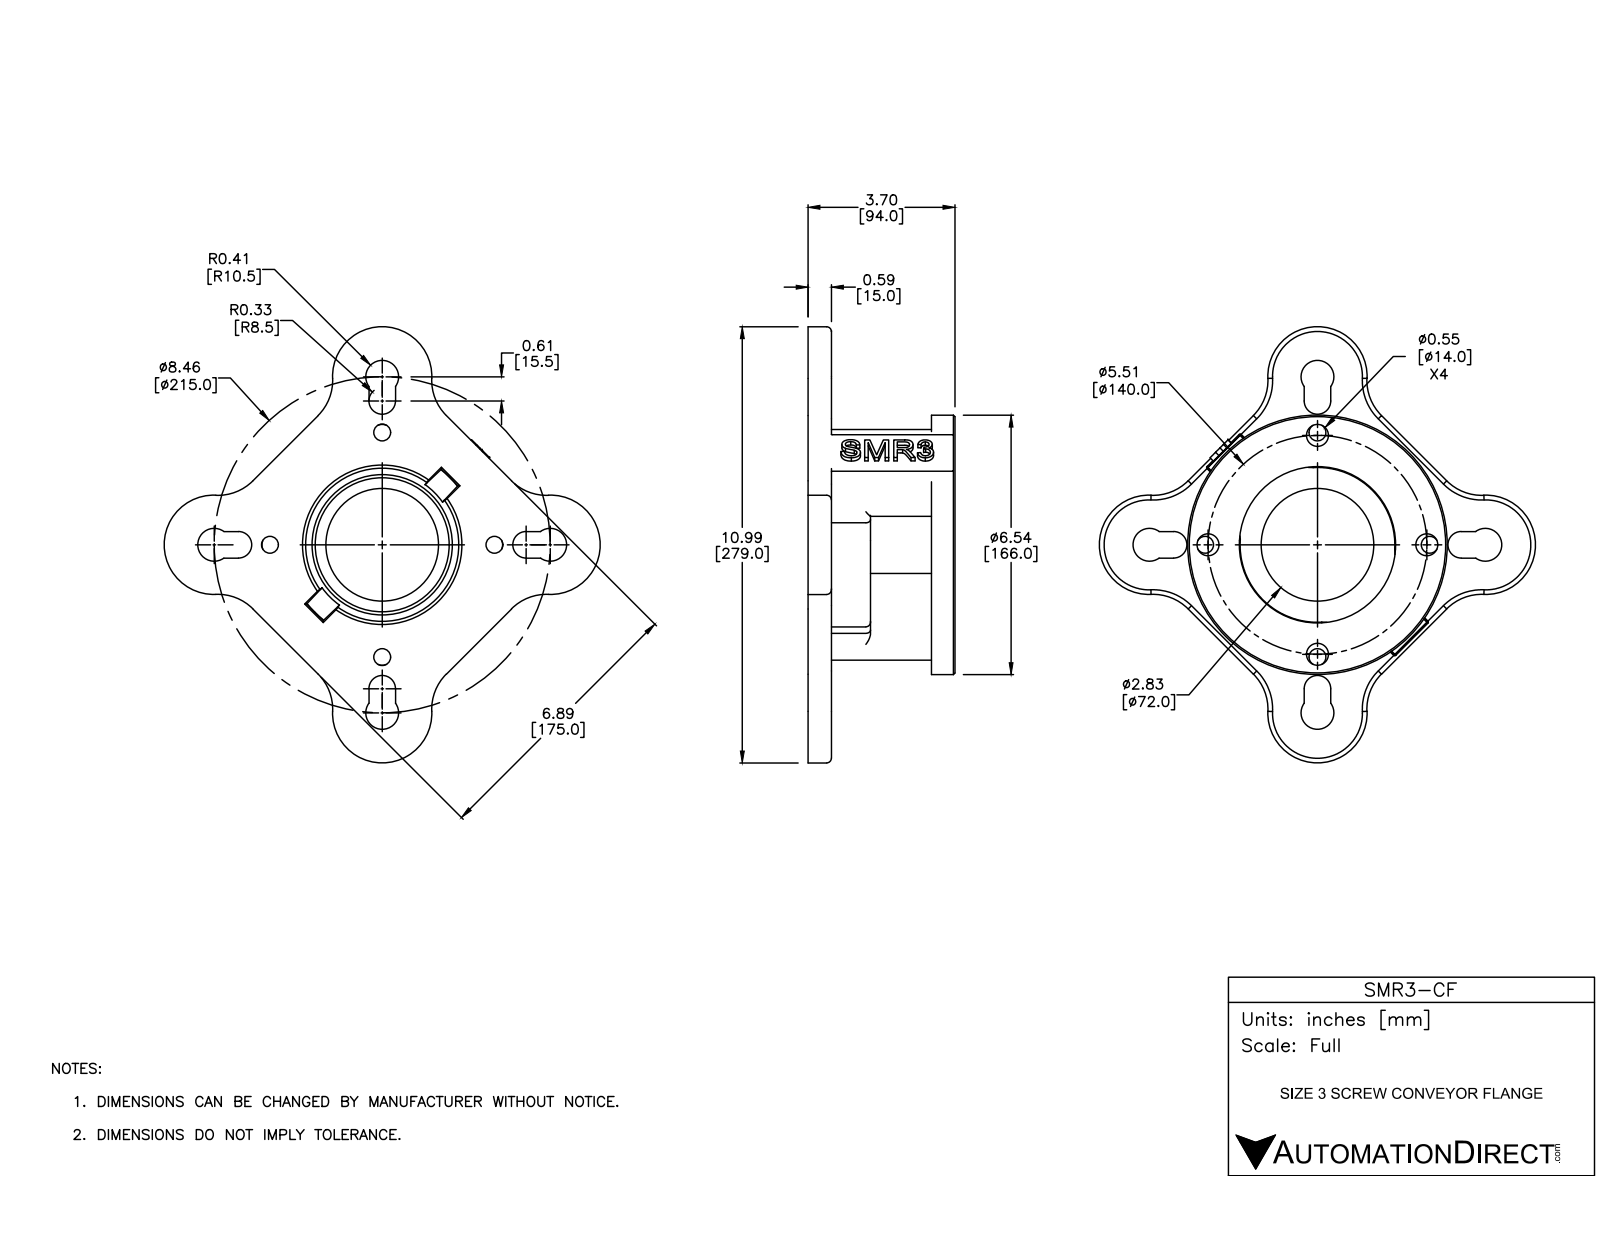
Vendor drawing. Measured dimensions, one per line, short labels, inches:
name: SMR3-CF
written by: SolidWorks 2016 (AUTOMOTIVE_DESIGN)
unit: in
bodies: 1 solid, 267 faces (79 planar, 104 cylindrical, 84 other)
size: 10.985 × 10.985 × 3.701
volume: 57.91 in³; area: 232.9 in²
holes: 4× ⌀0.422, 4× ⌀0.551, 1× ⌀2.835, 1× ⌀3.375, 1× ⌀3.858, 1× ⌀3.937
bosses: 1× ⌀6.535
rounds: 16× R0.02, 12× R1.25, 8× R0.394, 6× R0.118, 4× R0.335, 4× R0.413, 4× R0.591, 1× R2.067
face distances: 0.591, 3.11, 3.701, 2.52, 1.535, 2.126, 0.984, 1.575, 1.378, 5.314
hole spacings: 3.949, 0.072, 2.756, 2.828, 3.897, 4, 5.584, 5.512
